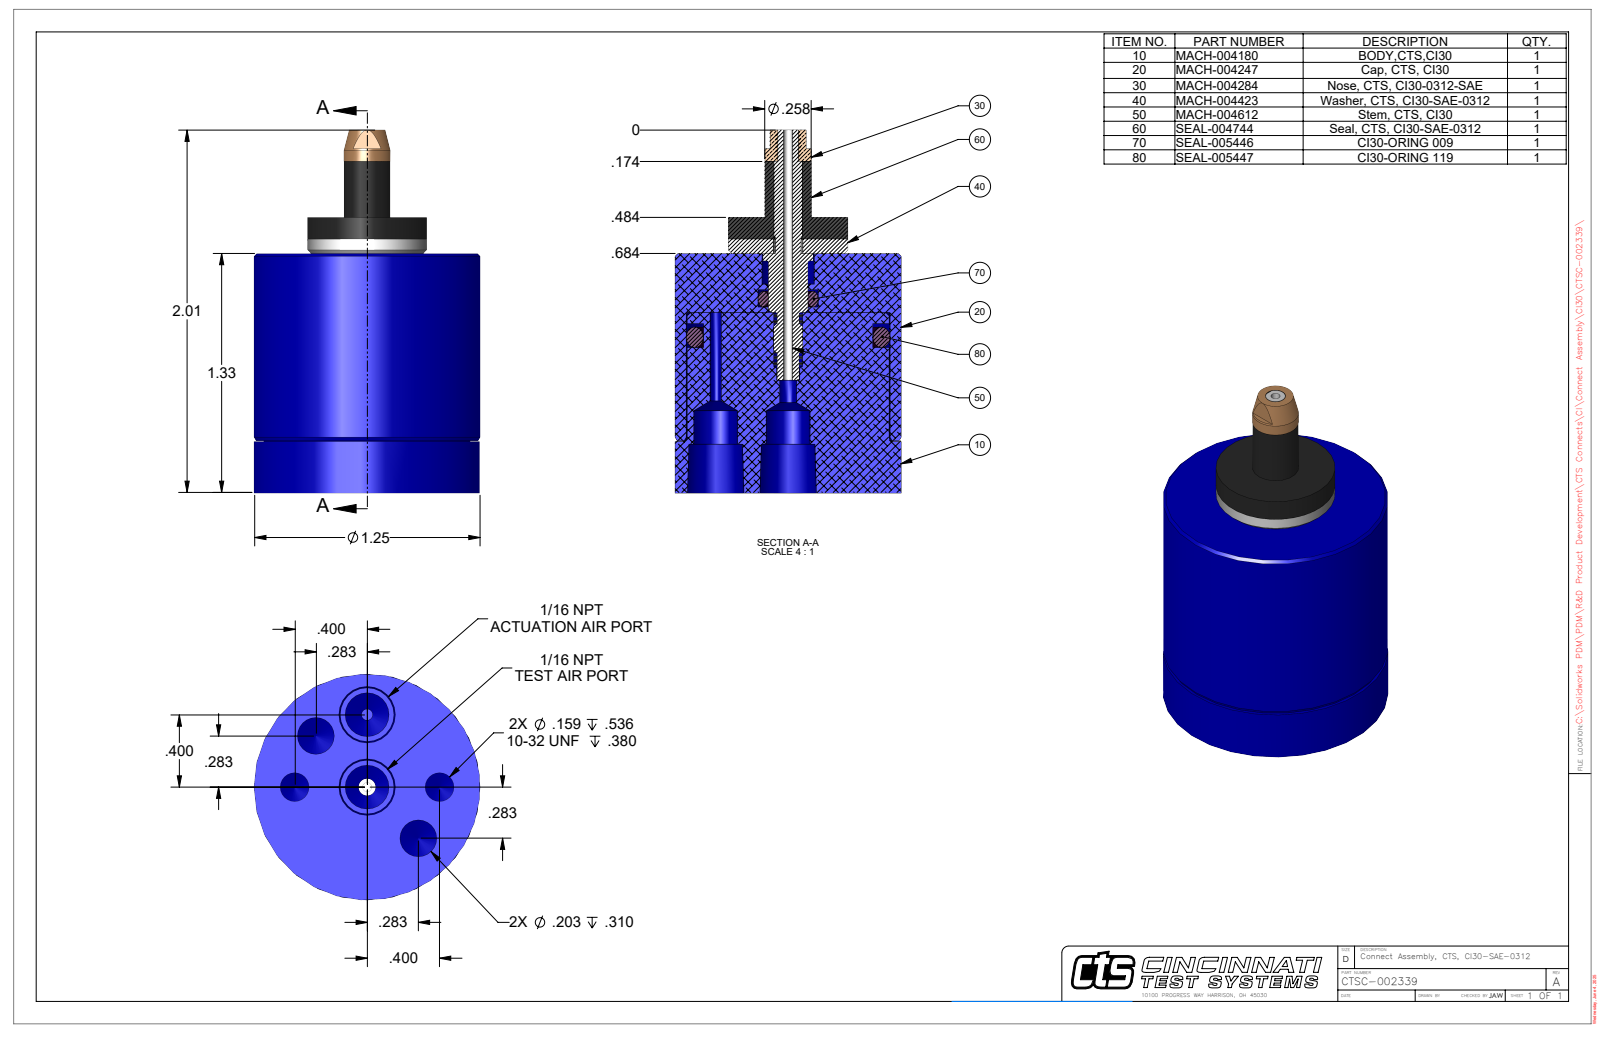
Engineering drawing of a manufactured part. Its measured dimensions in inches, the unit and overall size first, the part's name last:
Units: inches
Overall size (bounding box): 2.009 × 1.25 × 1.25
Round holes (diameter × count): ⌀0.159 ×2, ⌀0.203 ×2, ⌀0.242 ×2, ⌀0.052 ×1, ⌀0.062 ×1, ⌀0.094 ×1, ⌀0.113 ×1, ⌀0.289 ×1, ⌀1.125 ×1
Round bosses / shafts (diameter × count): ⌀1.25 ×1, ⌀1.115 ×1, ⌀0.66 ×1, ⌀0.277 ×1, ⌀0.257 ×1
Main face-to-face distances: 1.325, 0.2, 1.525, 0.287, 1.039, 1.239, 0.29, 1.035, 1.235, 0.271
Hole centre spacings: 0.306, 0.4, 0.739, 0.4, 0.566, 0.8, 0.8
Volume: 1.604 in³ · Surface area: 13.23 in²
Bodies: 2 solids, 90 faces (22 planar, 36 cylindrical, 32 other)
Part name (STEP PRODUCT): CTSC-002339
STEP written by: SolidWorks 2023 (AUTOMOTIVE_DESIGN)
